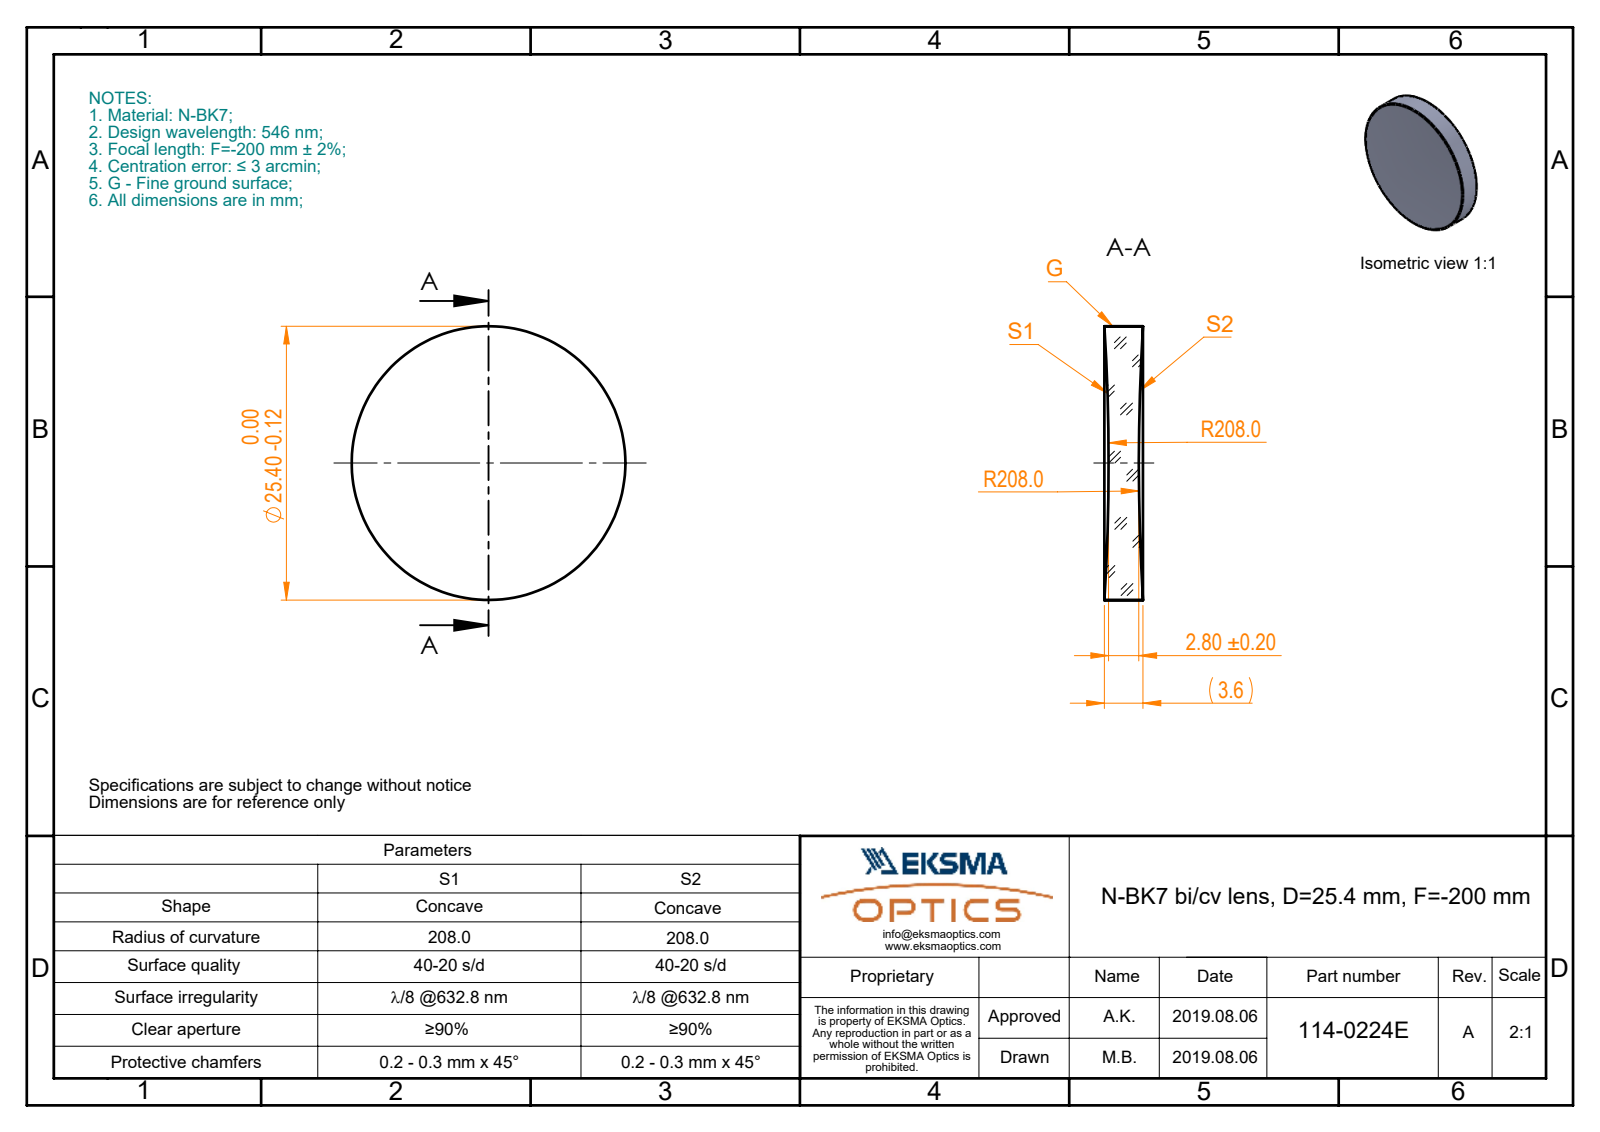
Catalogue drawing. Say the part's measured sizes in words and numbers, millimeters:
The part is named "114-0224E BK7 bi-cv 25.4 F-200". Its 3-D file was written by "SolidWorks 2017 (CONFIG_CONTROL_DESIGN)". It is 1 solid with 6 faces: 0 planar, 2 cylindrical and 4 other. Overall it measures 25.4 by 25.4 by 3.58 millimeters. Its volume is 1 615 cubic millimeters and its surface area 1 300 square millimeters. Round bosses or shafts: 1 of diameter 25.4.
